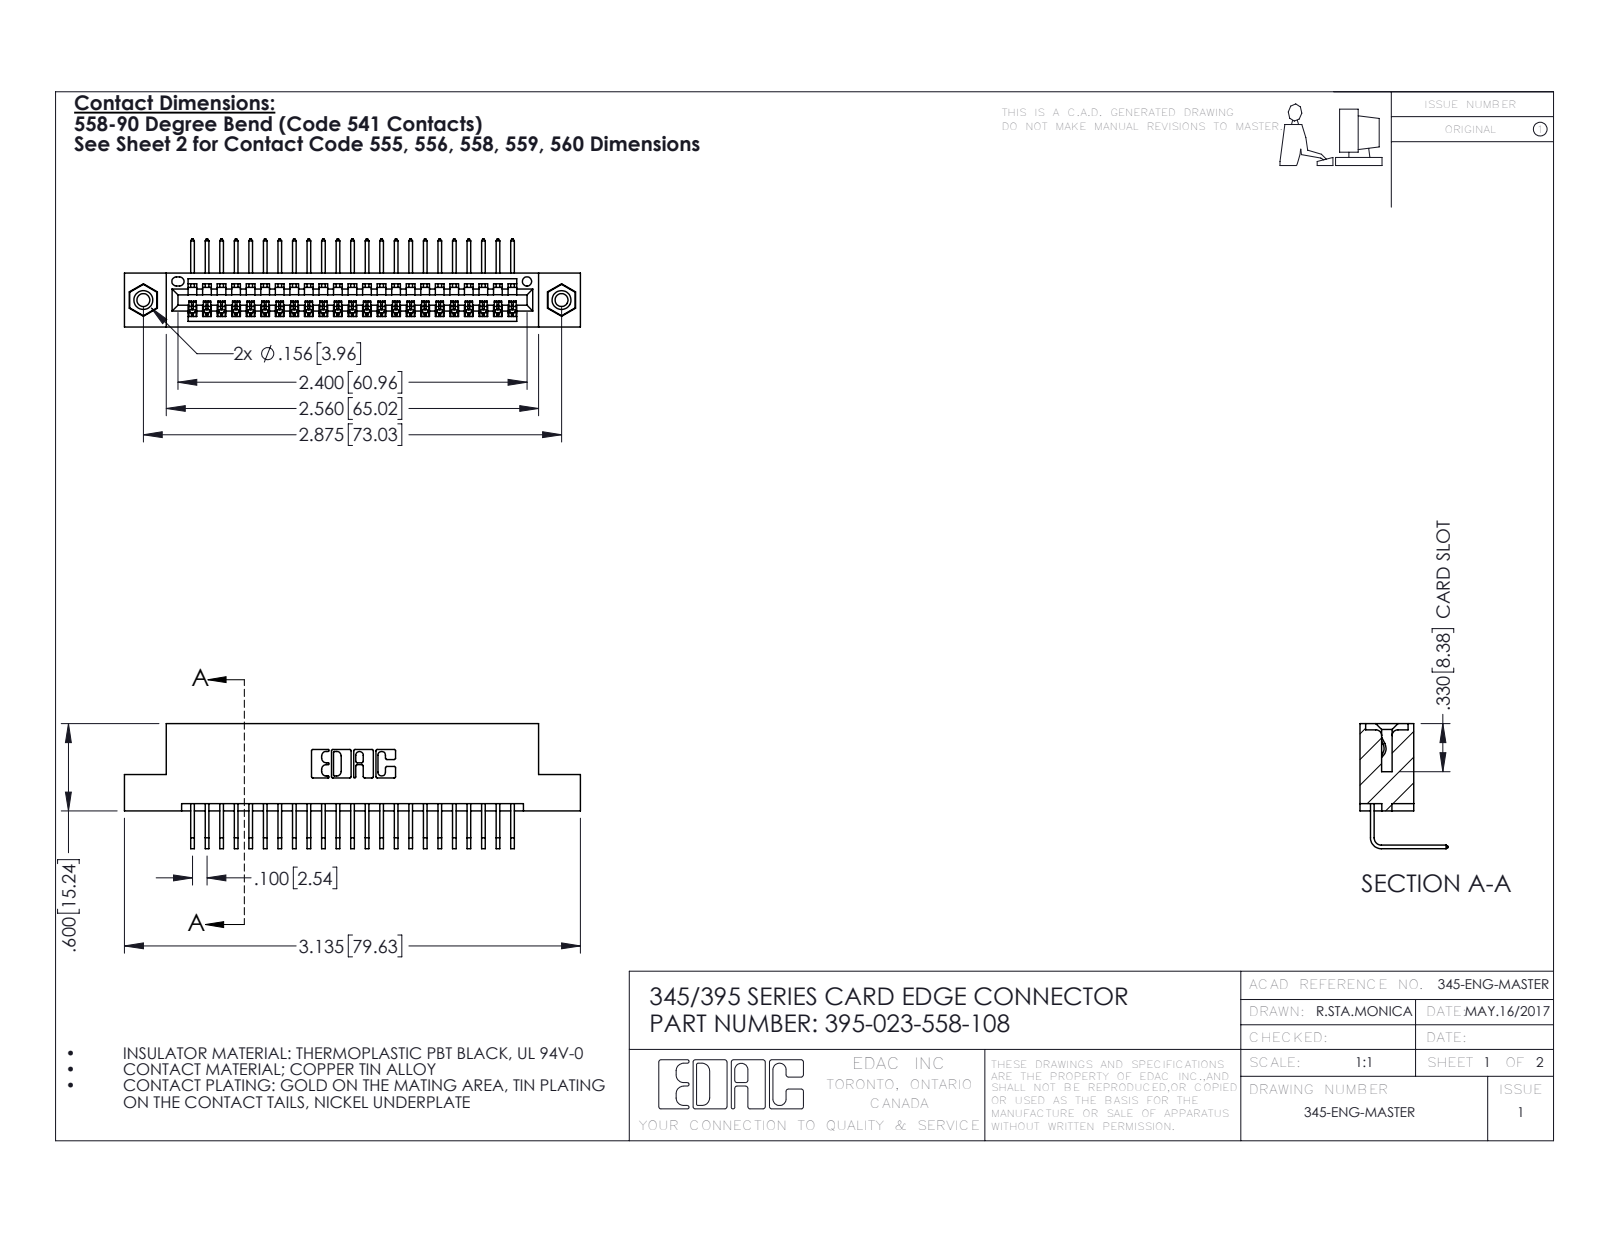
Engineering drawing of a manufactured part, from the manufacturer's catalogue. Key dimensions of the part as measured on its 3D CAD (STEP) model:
Part name (STEP PRODUCT): 345-250-001_345-250-003-102; 395-023-558-108; 345 Part_Flush Mounting Lugs - 0.156 Dia-TI; 345-292-001_558 Tail - 2
STEP written by: SolidWorks 2016 (CONFIG_CONTROL_DESIGN)
Units: inches
Bodies: 26 solids, 1566 faces (1078 planar, 472 cylindrical, 16 other)
Overall size (bounding box): 3.135 × 0.859 × 0.605
Volume: 0.456 in³ · Surface area: 15.73 in²
Round holes (diameter × count): ⌀0.089 ×2, ⌀0.125 ×2, ⌀0.156 ×2, ⌀0.064 ×1
Round bosses / shafts (diameter × count): ⌀0.155 ×2
Partial cylindrical surfaces — rounded edges, fillets, slot ends (radius × count): R0.006 ×46, R0.01 ×22, R0.007 ×6, R0.031 ×6, R0.026 ×3, R0.031 ×2, R0.04 ×2, R0.014 ×1
Main face-to-face distances: 0.072, 0.298, 0.2, 0.37, 0.098, 0.272, 0.025, 0.225, 0.149, 0.072
Hole centre spacings: 0.27, 2.641, 2.875
